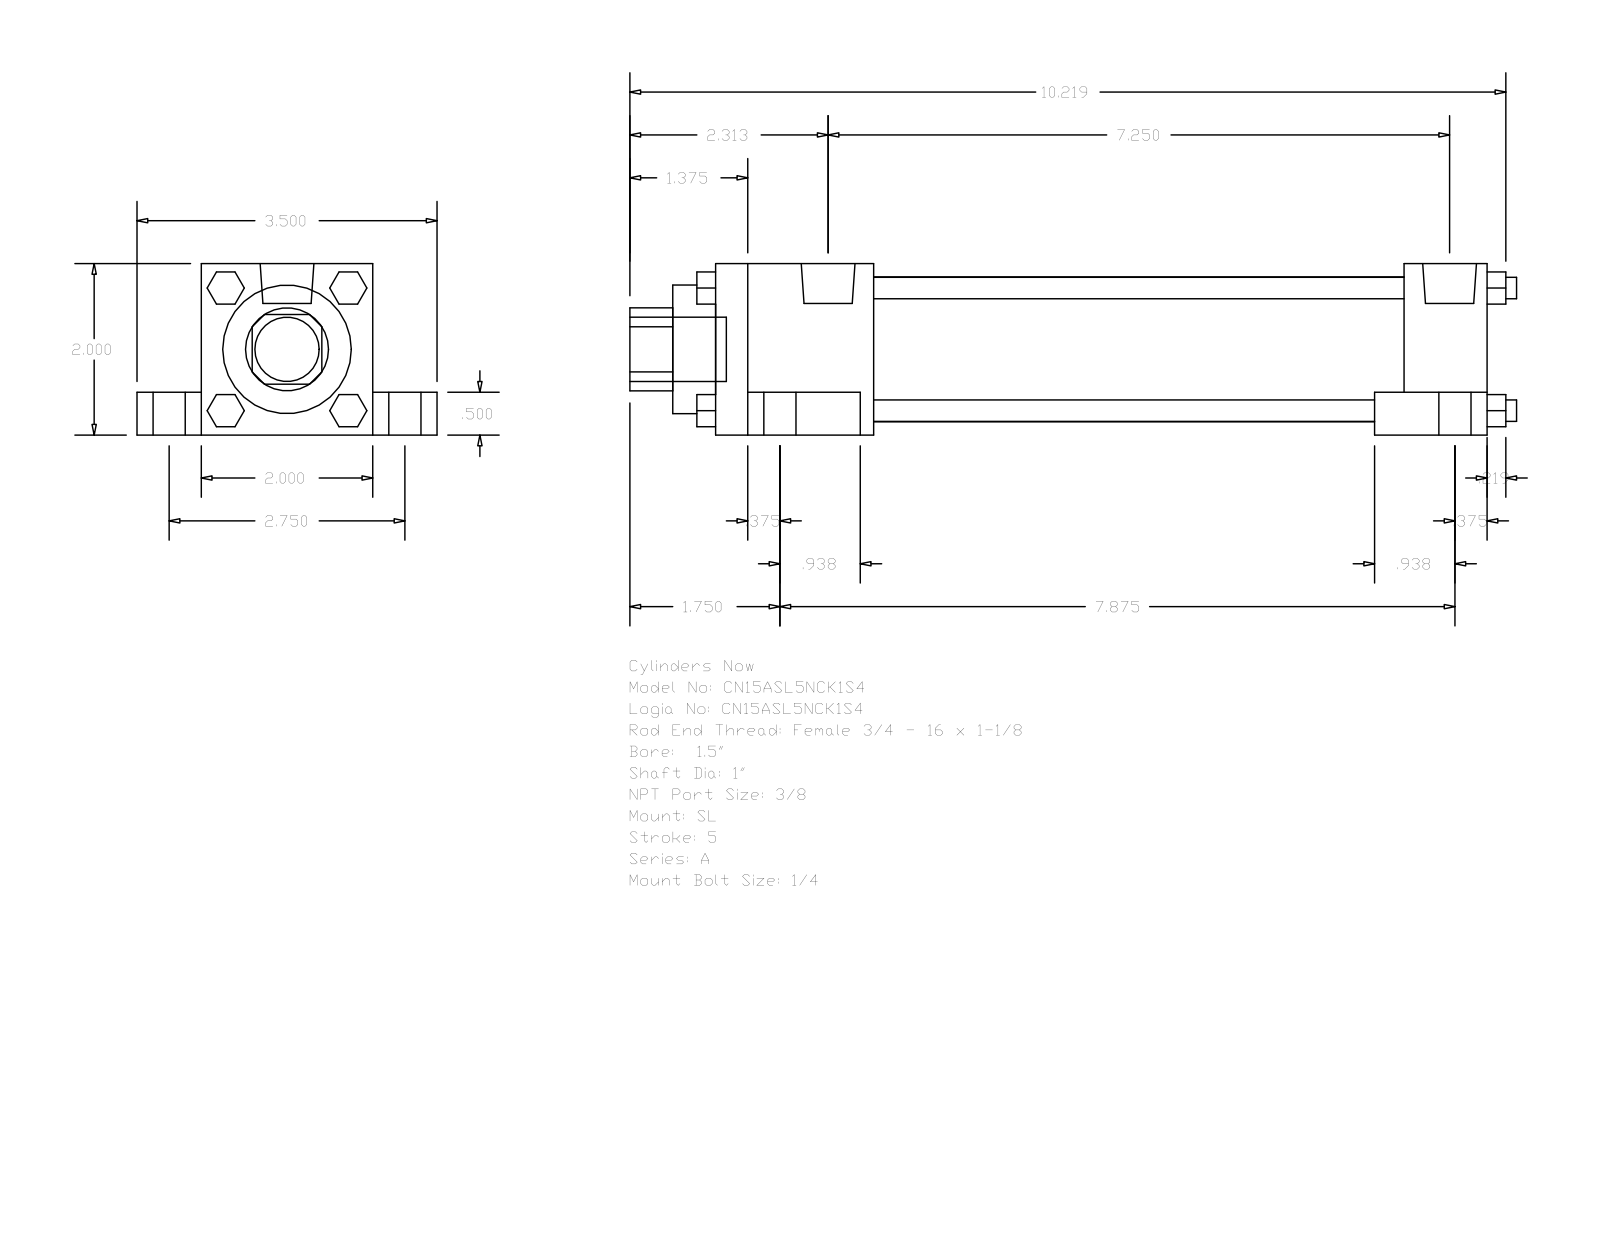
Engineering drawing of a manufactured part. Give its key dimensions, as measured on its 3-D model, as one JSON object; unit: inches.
{"part_name": "A_SL__0150_1", "step_written_by": "GSSL Pune (CONFIG_CONTROL_DESIGN)", "units": "inches", "bodies": {"solids": 0, "faces": 148, "planar": 112, "cylindrical": 36, "other": 0}, "overall_size": [10.344, 3.5, 2], "round_holes": [[1, 1], [1.5, 1], [1.69, 1]], "round_bosses_or_shafts": [[0.625, 4], [0.375, 4], [0.25, 4], [0.219, 4], [0.627, 2], [0.75, 1]], "partial_cylinders_radius": [[0.484, 1]], "face_to_face_distances": [2, 0.5, 1.5, 0.75, 2.75, 0.375, 9, 1.313, 8.031, 0.969]}
